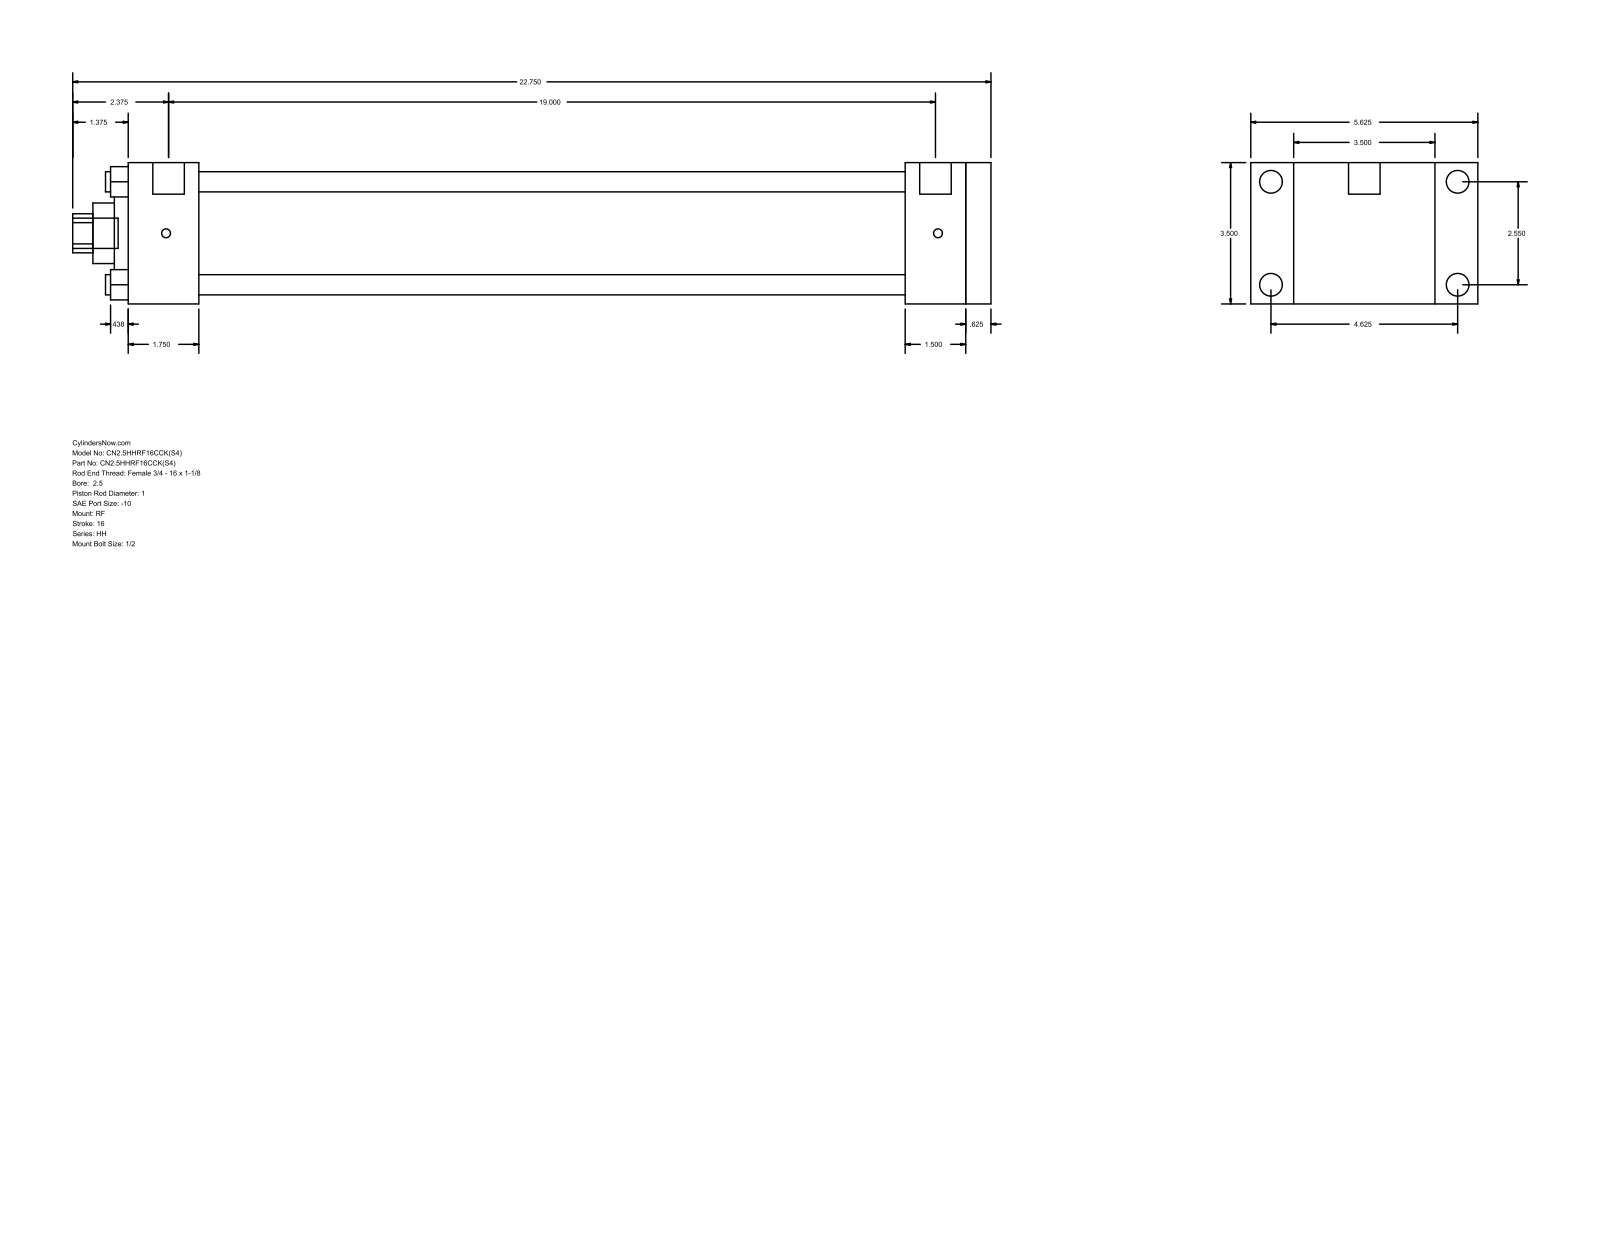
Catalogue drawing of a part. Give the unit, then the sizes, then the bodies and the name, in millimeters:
Units: millimetres
Overall size (bounding box): 577.85 × 142.88 × 88.9
Round holes (diameter × count): ⌀12.7 ×4, ⌀25.4 ×1, ⌀38.1 ×1, ⌀60.33 ×1, ⌀73.03 ×1
Round bosses / shafts (diameter × count): ⌀14.3 ×4, ⌀5.56 ×4, ⌀19.84 ×2, ⌀19.05 ×1
Partial cylindrical surfaces — rounded edges, fillets, slot ends (radius × count): R12.29 ×1
Main face-to-face distances: 88.9, 15.87, 527.06, 542.93, 44.46, 482.6, 498.47, 488.96, 444.5, 38.1
Hole centre spacings: 45.79, 64.76, 91.58
Bodies: 0 solids, 94 faces (65 planar, 29 cylindrical, 0 other)
Part name (STEP PRODUCT): HH_RF__0250_1
STEP written by: GSSL Pune (CONFIG_CONTROL_DESIGN)
